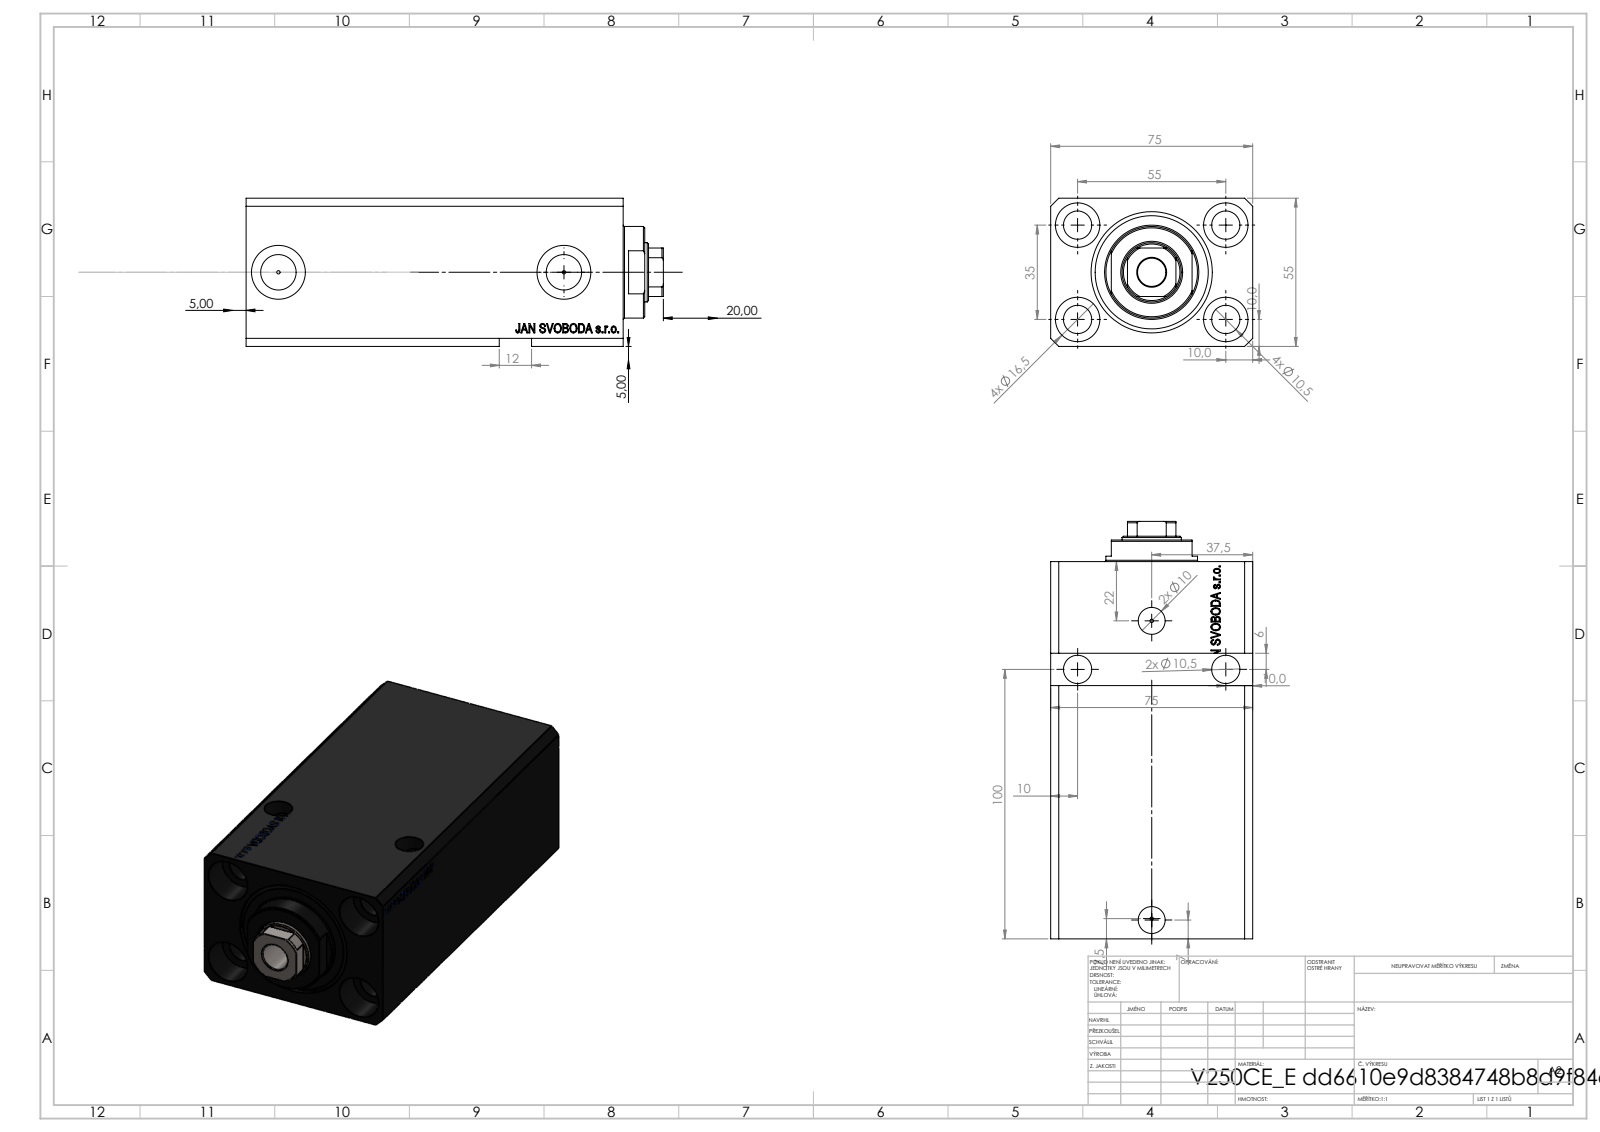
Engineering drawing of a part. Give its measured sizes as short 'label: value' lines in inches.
name: V250CE_C_VCP; V250CE_E_Body; V250CE_VC_E
written by: SolidWorks 2019 (CONFIG_CONTROL_DESIGN)
unit: in
bodies: 3 solids, 914 faces (438 planar, 104 cylindrical, 372 other)
size: 6.102 × 2.953 × 2.165
volume: 28.63 in³; area: 158.1 in²
holes: 9× ⌀0.413, 4× ⌀0.049, 4× ⌀0.65, 2× ⌀0.394, 2× ⌀0.518, 2× ⌀0.787, 1× ⌀0.866, 1× ⌀1.26, 1× ⌀1.772
bosses: 1× ⌀1.339
rounds: 1× R0.413
face distances: 2.165, 2.953, 0.591, 5.512, 4.921, 0.39, 4.531, 5.122, 0.433, 5.079
hole spacings: 1.283, 1.294, 2.165, 3.818, 1.283, 1.378, 2.567, 2.953
